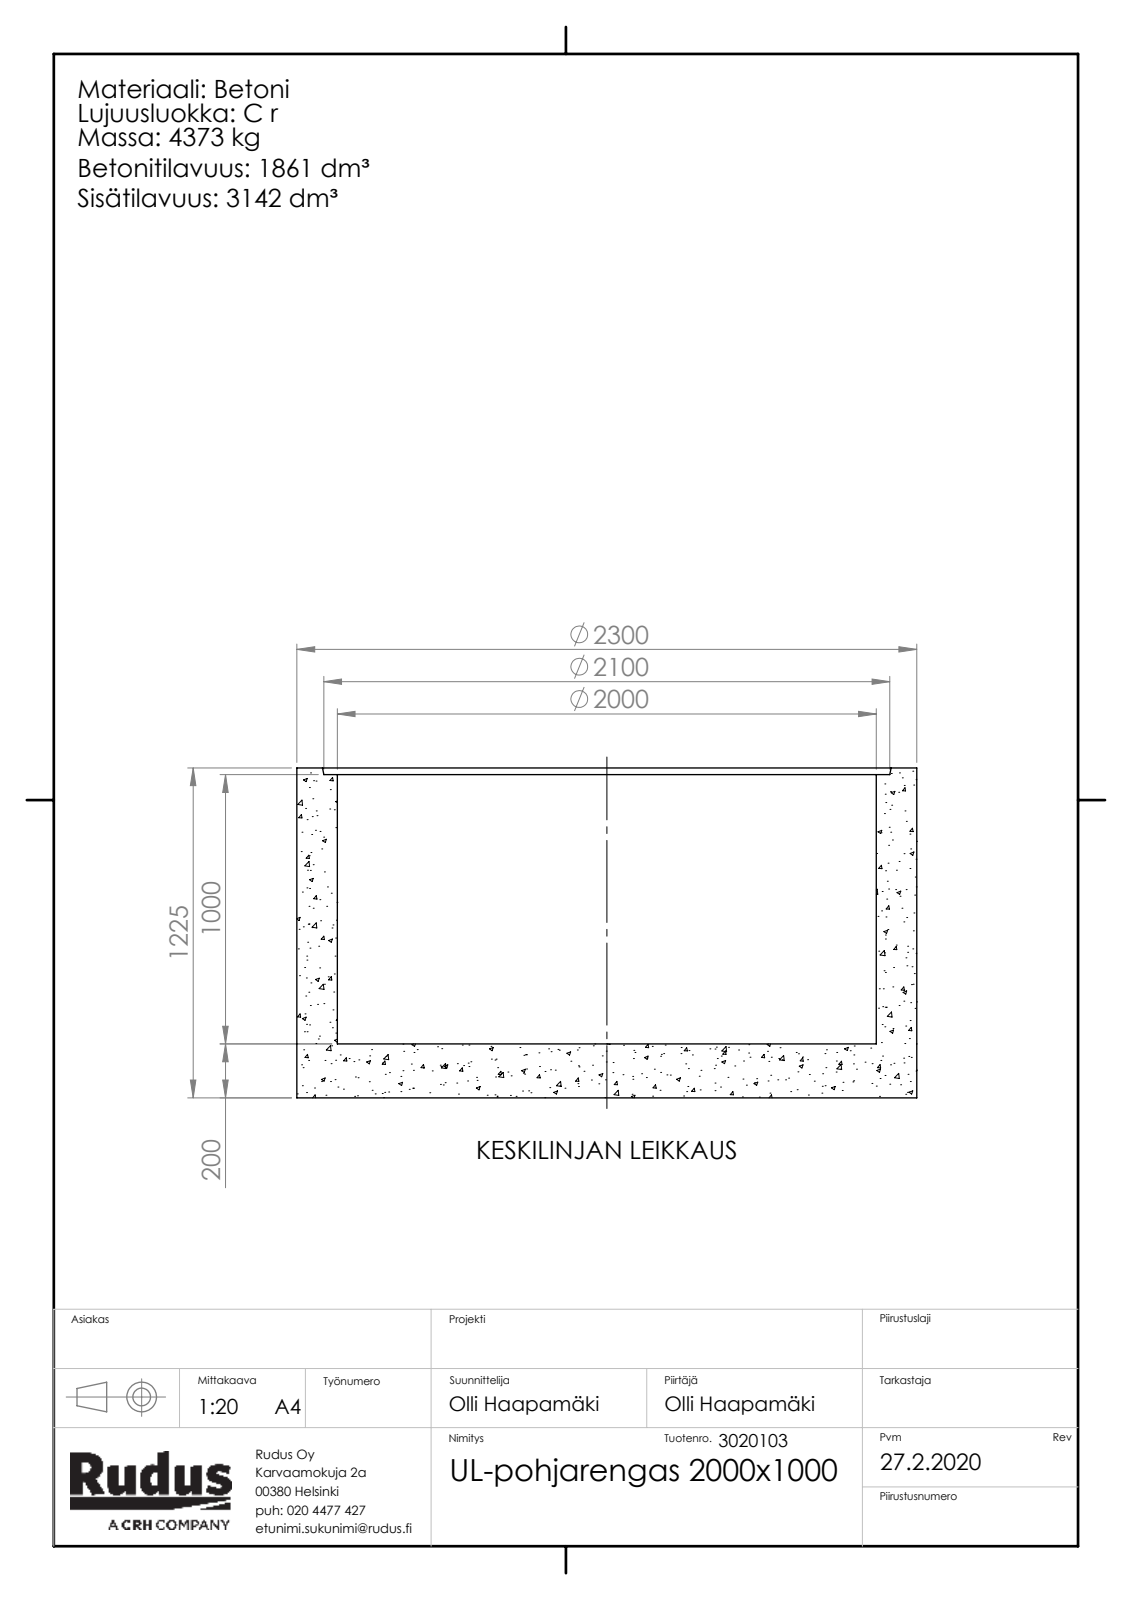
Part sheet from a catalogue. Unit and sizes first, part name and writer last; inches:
Units: inches
Overall size (bounding box): 90.551 × 90.551 × 48.228
Round bosses / shafts (diameter × count): ⌀90.551 ×1
Main face-to-face distances: 7.874, 48.228, 40.354, 47.244, 39.37, 0.984, 30.353, 22.479, 16.891, 17.876
Volume: 113 600 in³ · Surface area: 36 550 in²
Bodies: 1 solid, 89 faces (6 planar, 2 cylindrical, 81 other)
Part name (STEP PRODUCT): EK-osa-kaivorunko_UL-pohjarengas; Rudus 3020103 UL-pohjarengas 2000x1000
STEP written by: SolidWorks 2019 (CONFIG_CONTROL_DESIGN)
